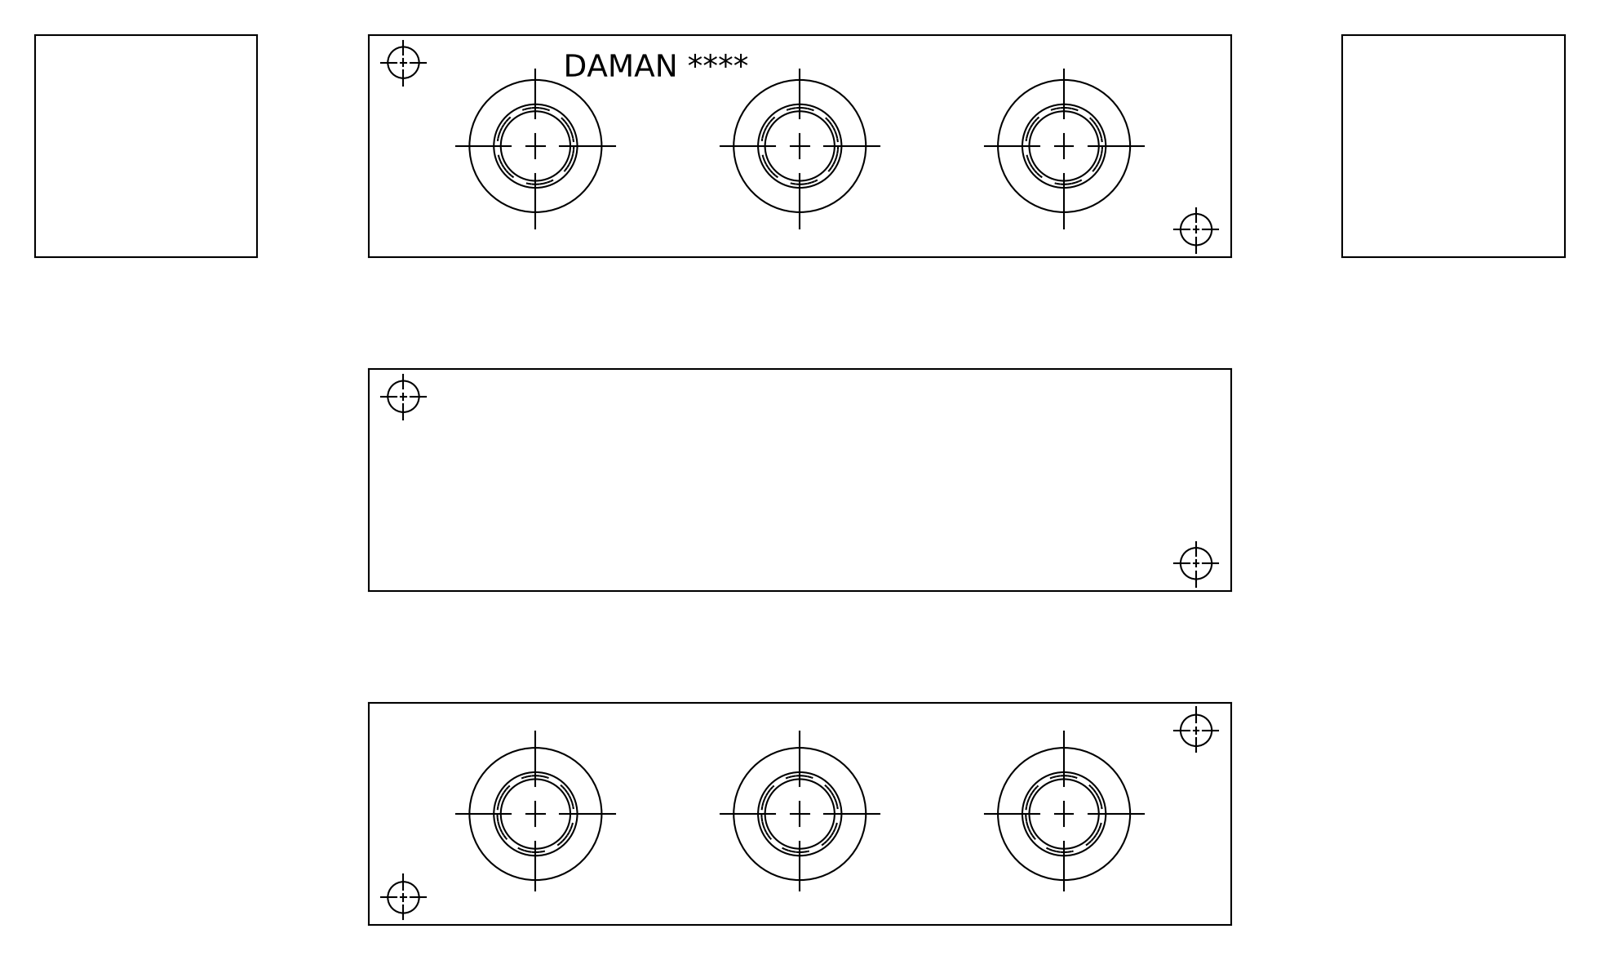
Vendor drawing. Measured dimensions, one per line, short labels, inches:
name: Part_AJ1800308S_3D
written by: Autodesk Inventor 2019 (AUTOMOTIVE_DESIGN)
unit: in
bodies: 1 solid, 406 faces (221 planar, 38 cylindrical, 147 other)
size: 7.75 × 2 × 2
volume: 28.06 in³; area: 88.44 in²
holes: 4× ⌀0.281, 3× ⌀0.625, 3× ⌀0.689, 3× ⌀0.75, 3× ⌀0.758, 3× ⌀1.206
face distances: 2, 7.75, 0.031, 1.969, 1.938, 1.407, 0.593, 0.562, 1.376, 0.814
hole spacings: 1.405, 5.985, 7.283, 2.375, 2.375, 3.641, 3.641, 4.75
